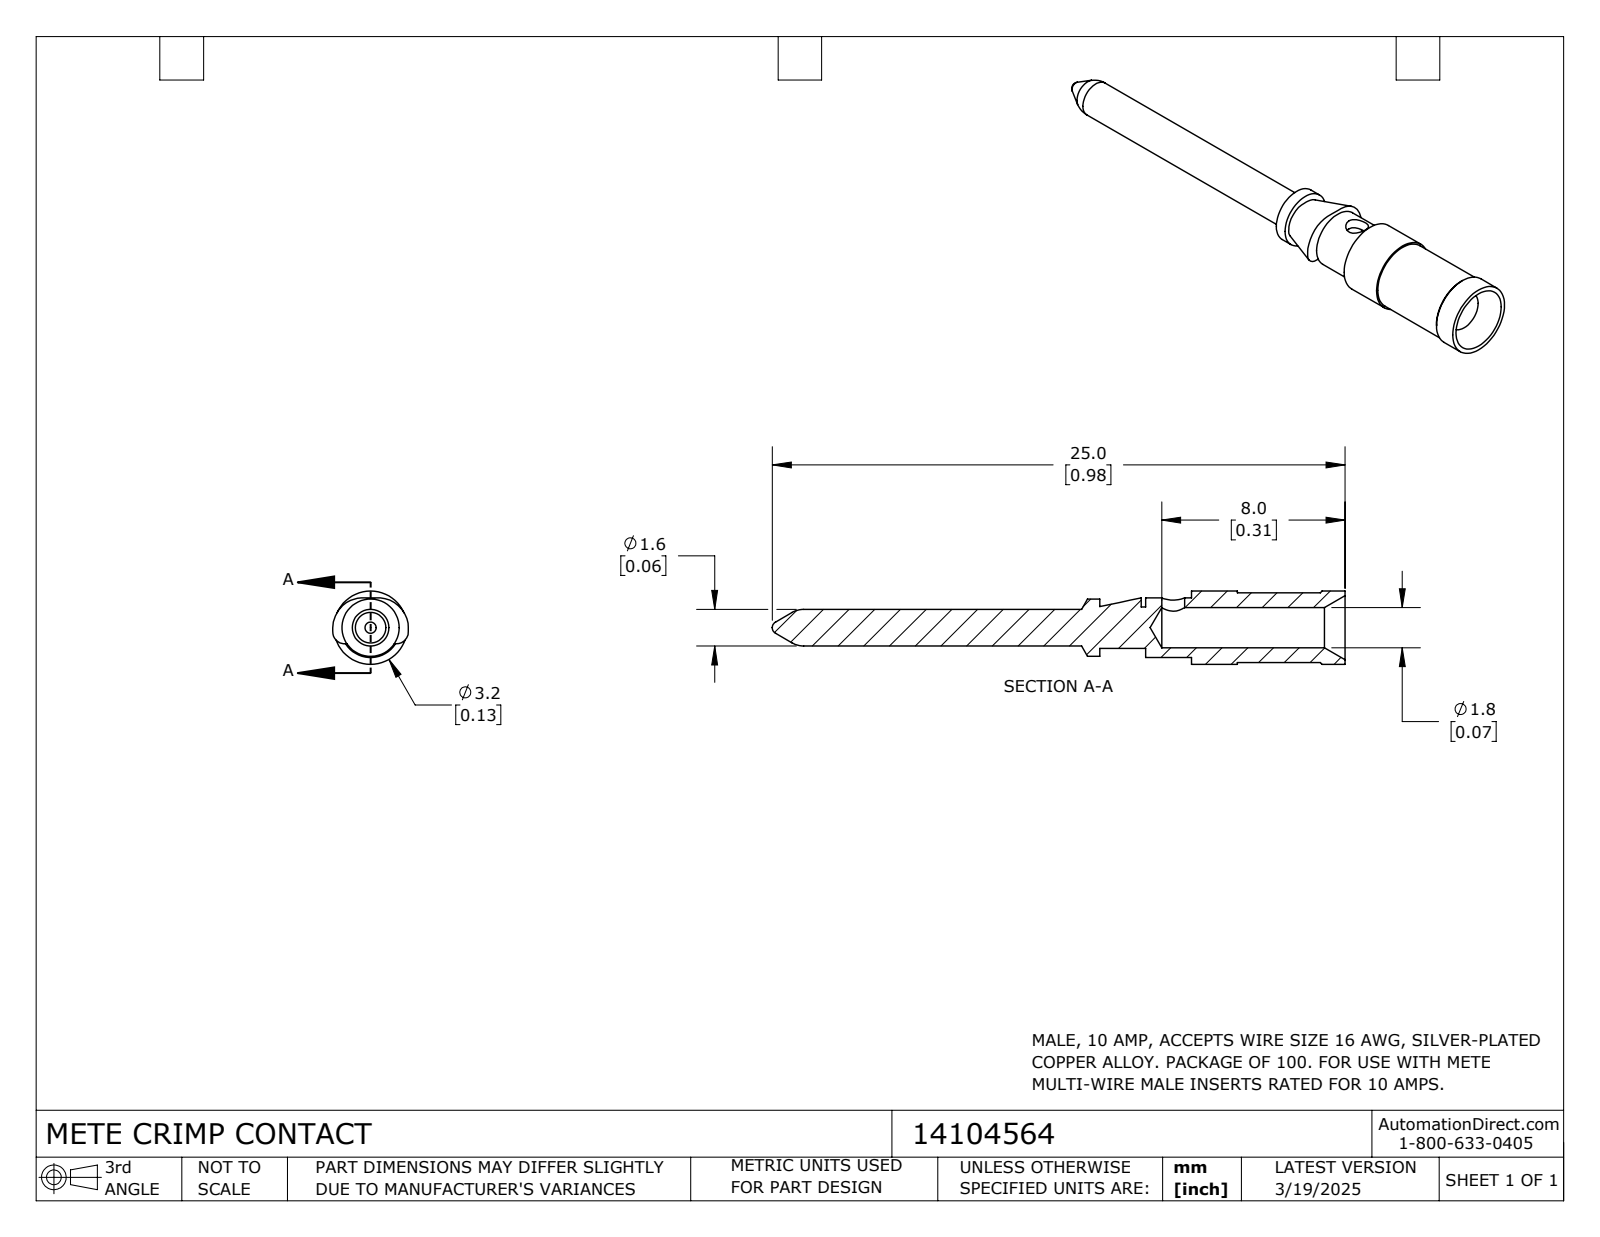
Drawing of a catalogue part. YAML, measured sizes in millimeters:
part_name: "14104564"
step_written_by: "SolidWorks 2024 (CONFIG_CONTROL_DESIGN)"
units: millimeters
bodies: {solids: 1, faces: 40, planar: 7, cylindrical: 18, other: 15}
overall_size: [25, 3.3, 3.2]
volume: 78
surface_area: 234
round_holes:
  - {diameter: 1, count: 1}
  - {diameter: 1.75, count: 1}
round_bosses_or_shafts:
  - {diameter: 3.2, count: 1}
  - {diameter: 3.05, count: 1}
  - {diameter: 2.6, count: 1}
  - {diameter: 2.5, count: 1}
  - {diameter: 1.8, count: 1}
  - {diameter: 1.6, count: 1}
face_to_face_distances: [2, 2.2, 4, 1.8, 6.7, 8.7, 8.9, 10.7, 4.7, 4.2]
